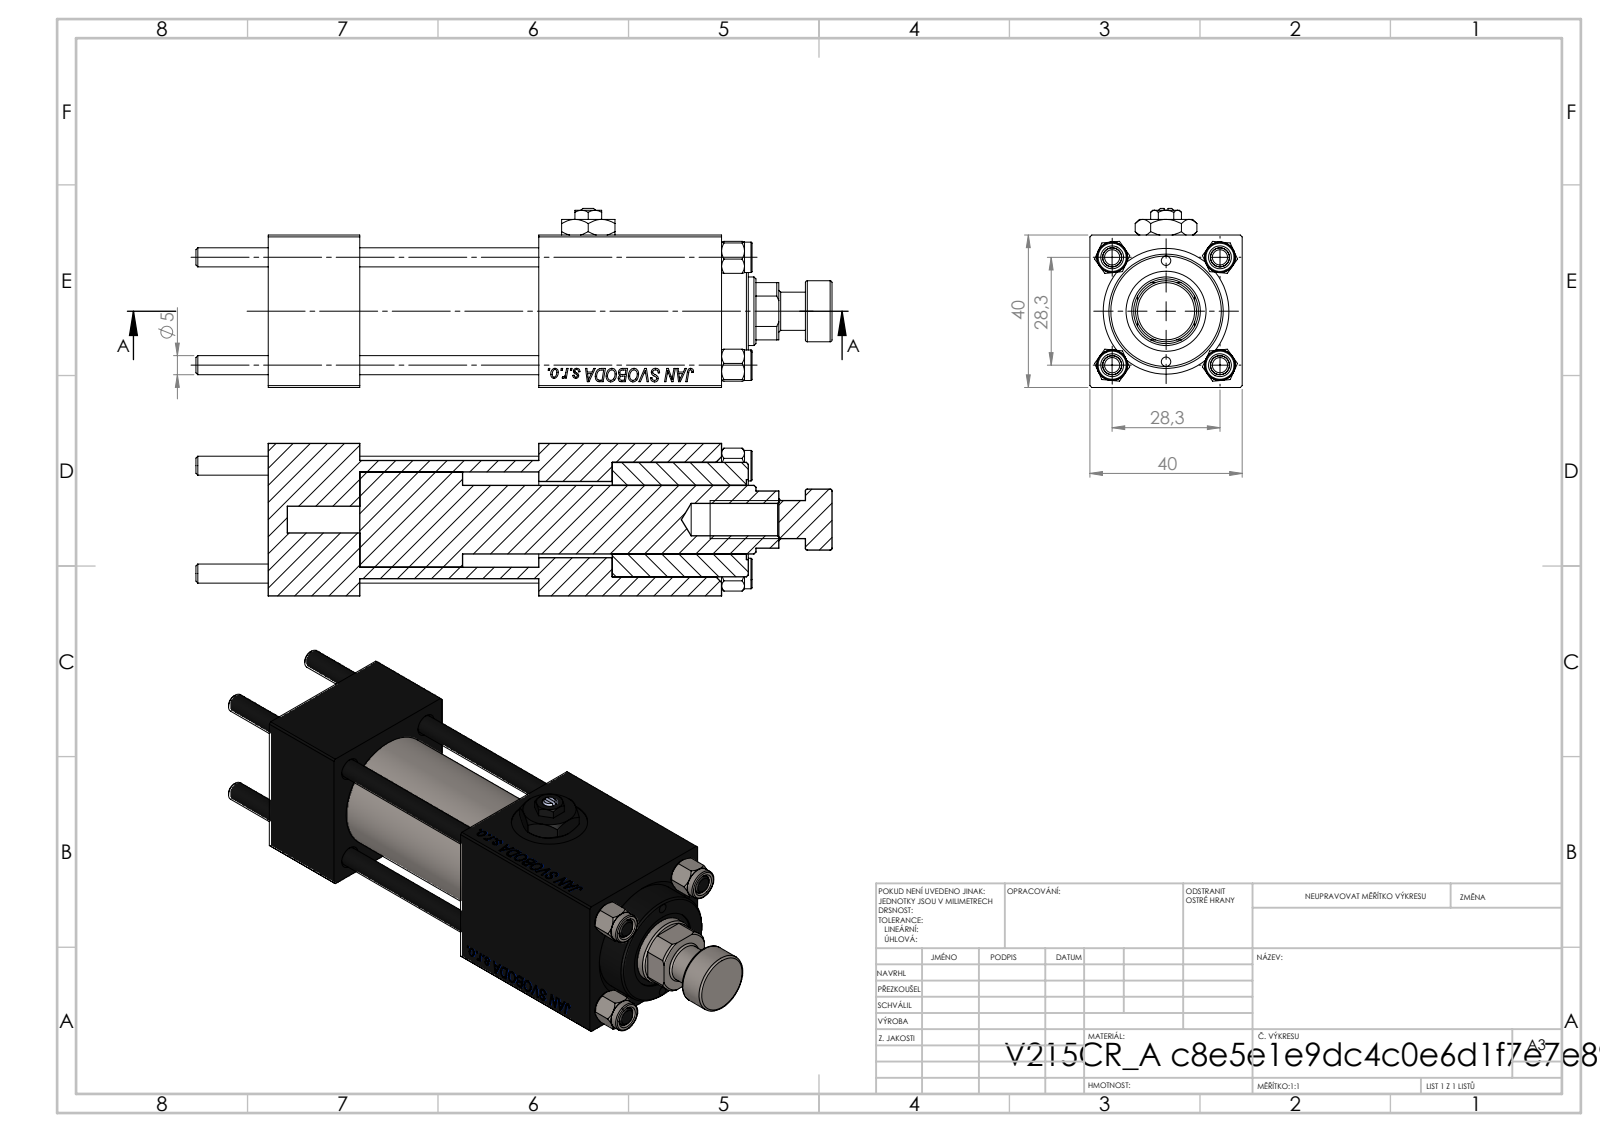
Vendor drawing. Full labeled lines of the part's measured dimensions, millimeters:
Part name (STEP PRODUCT): NUT_M5; V215_VC_A; V215CR_VCP; V215CR_ROD_END_W (+3 more)
STEP written by: SolidWorks 2019 (CONFIG_CONTROL_DESIGN)
Units: millimetres
Bodies: 13 solids, 1195 faces (545 planar, 88 cylindrical, 562 other)
Overall size (bounding box): 167 × 47 × 40
Volume: 153 618 mm³ · Surface area: 63 055 mm²
Round holes (diameter × count): ⌀5 ×4, ⌀20 ×3, ⌀2.5 ×2, ⌀7 ×2, ⌀13.16 ×2, ⌀8.5 ×1, ⌀18 ×1, ⌀21 ×1, ⌀25 ×1, ⌀30 ×1
Round bosses / shafts (diameter × count): ⌀8 ×4, ⌀31 ×1, ⌀16 ×1, ⌀10 ×1
Partial cylindrical surfaces — rounded edges, fillets, slot ends (radius × count): R8.5 ×1
Main face-to-face distances: 40, 24, 71, 47, 90.3, 66.3, 19.3, 119, 95, 48
Hole centre spacings: 14.18, 20.01, 28.3, 30.84, 13.25, 40.02, 26.5, 72
